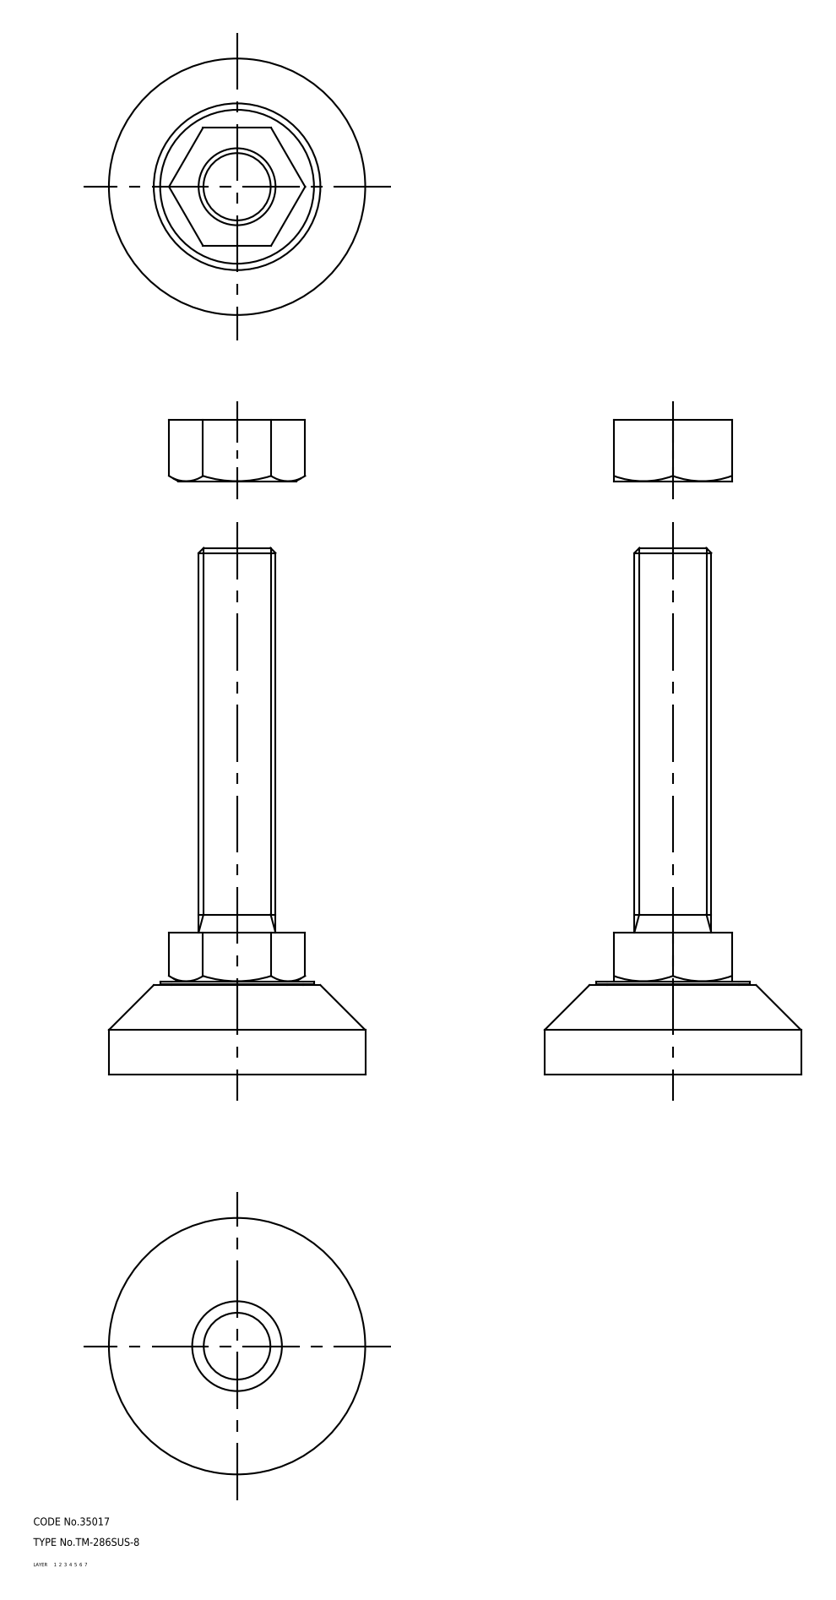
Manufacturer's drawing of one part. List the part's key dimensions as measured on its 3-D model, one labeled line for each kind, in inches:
Part name (STEP PRODUCT): 67111650; 67111663
STEP written by: CADfix (AUTOMOTIVE_DESIGN)
Units: inches
Bodies: 2 solids, 52 faces (0 planar, 0 cylindrical, 52 other)
Overall size (bounding box): 8.091 × 3.937 × 3.937
Volume: 24.33 in³ · Surface area: 80.05 in²
